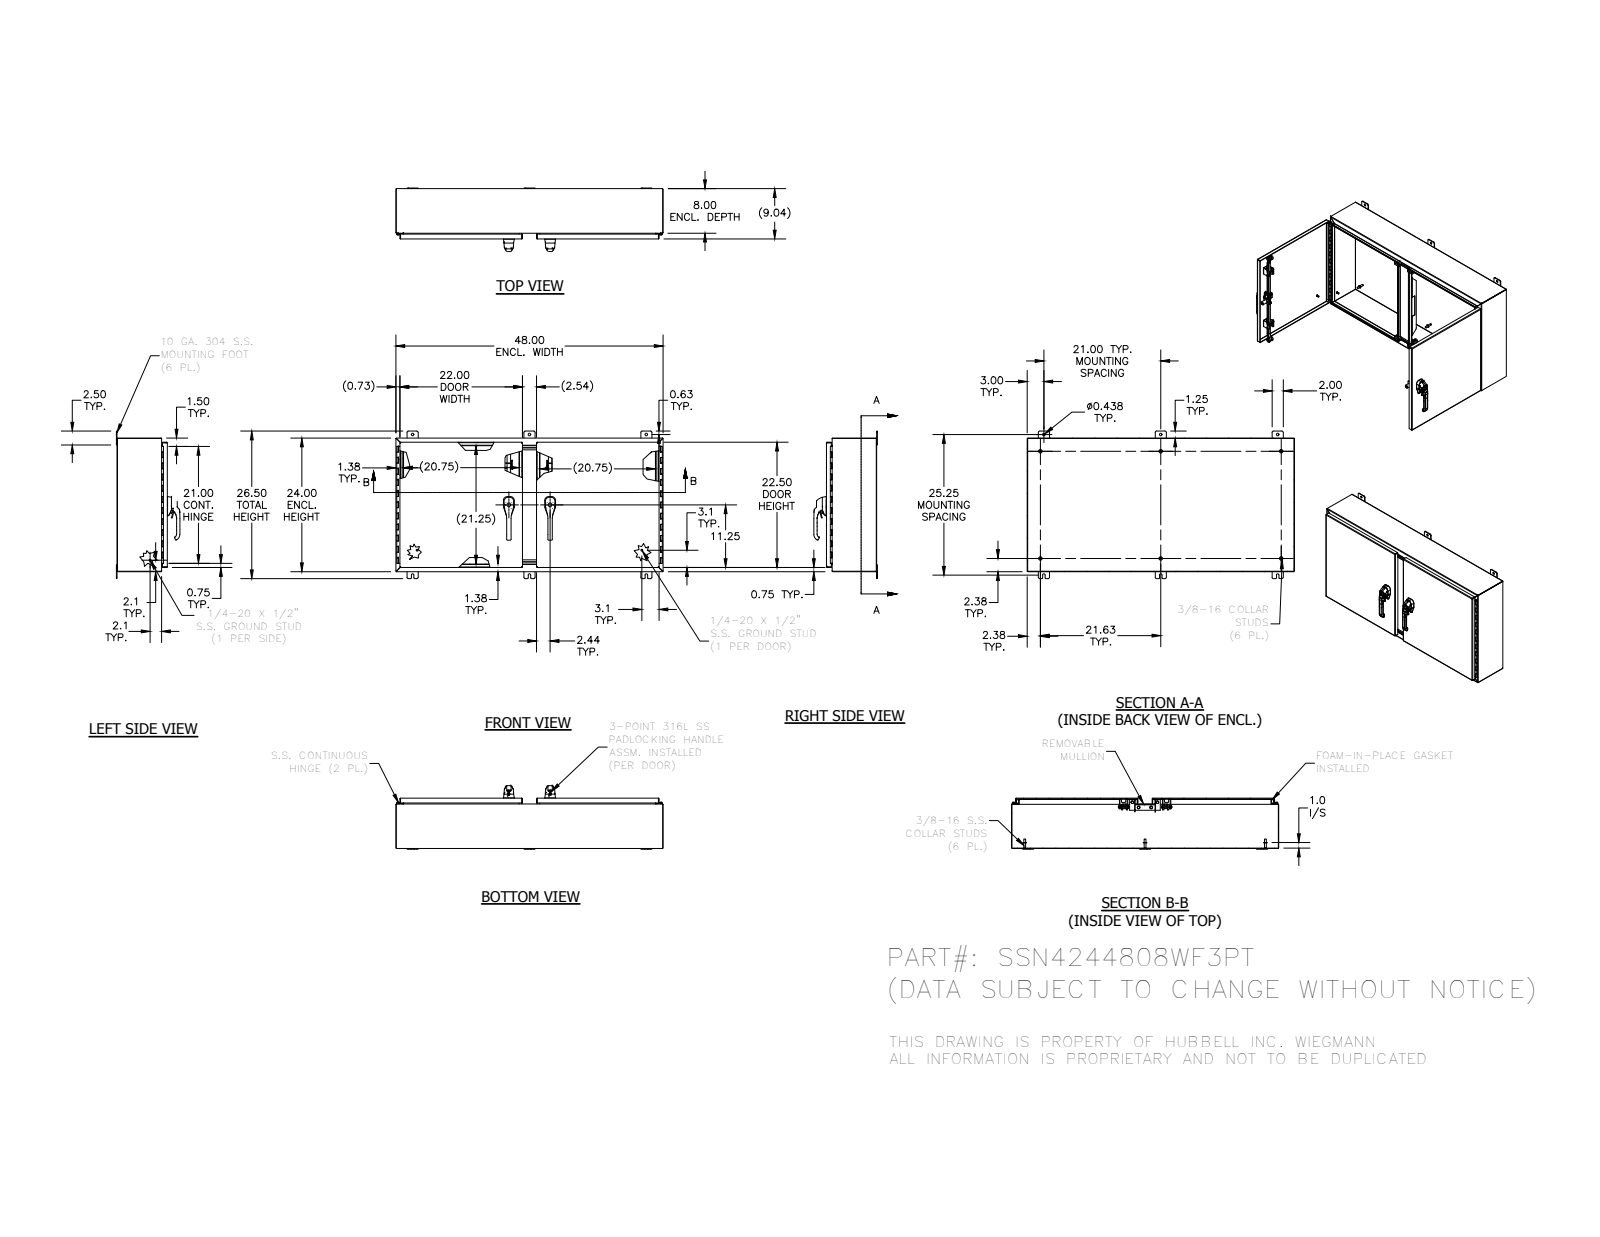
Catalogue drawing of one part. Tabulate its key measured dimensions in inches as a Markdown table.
| quantity | value |
| --- | --- |
| part name | SSN4244808WF3PT; HFW303115; SSN424WF3PTRML; HFW316325 (+8 more) |
| STEP written by | SolidWorks 2014 (AUTOMOTIVE_DESIGN) |
| units | inches |
| bodies | 125 solids, 6344 faces (2242 planar, 2586 cylindrical, 1516 other) |
| overall size | 48 × 26.5 × 11.409 |
| volume | 361.2 in³ |
| surface area | 8 762 in² |
| round holes (diameter × count) | 0.262 × 12, 0.187 × 8, 0.213 × 6, 0.28 × 6, 0.438 × 6, 0.196 × 4, 0.252 × 4, 0.281 × 4, 0.315 × 4, 0.4 × 4, 0.402 × 4, 0.45 × 4 |
| round bosses / shafts (diameter × count) | 0.25 × 9, 0.625 × 6, 0.533 × 6, 0.33 × 6, 0.236 × 5, 0.531 × 4, 0.438 × 4, 0.435 × 4 |
| partial cylindrical surfaces (radius × count) | 0.02 × 317, 0.012 × 221, 0.019 × 39, 0.031 × 33, 0.125 × 31, 0.05 × 30, 0.25 × 30, 0.079 × 25 |
| main face-to-face distances | 0.074, 0.094, 8.942, 8.868, 9.035, 8.961, 23.926, 7.926, 23.852, 47.926 |
| hole center spacings | 0.38, 0.76, 7.417, 0.492, 0.492, 0.886, 1.236, 1.376 |
